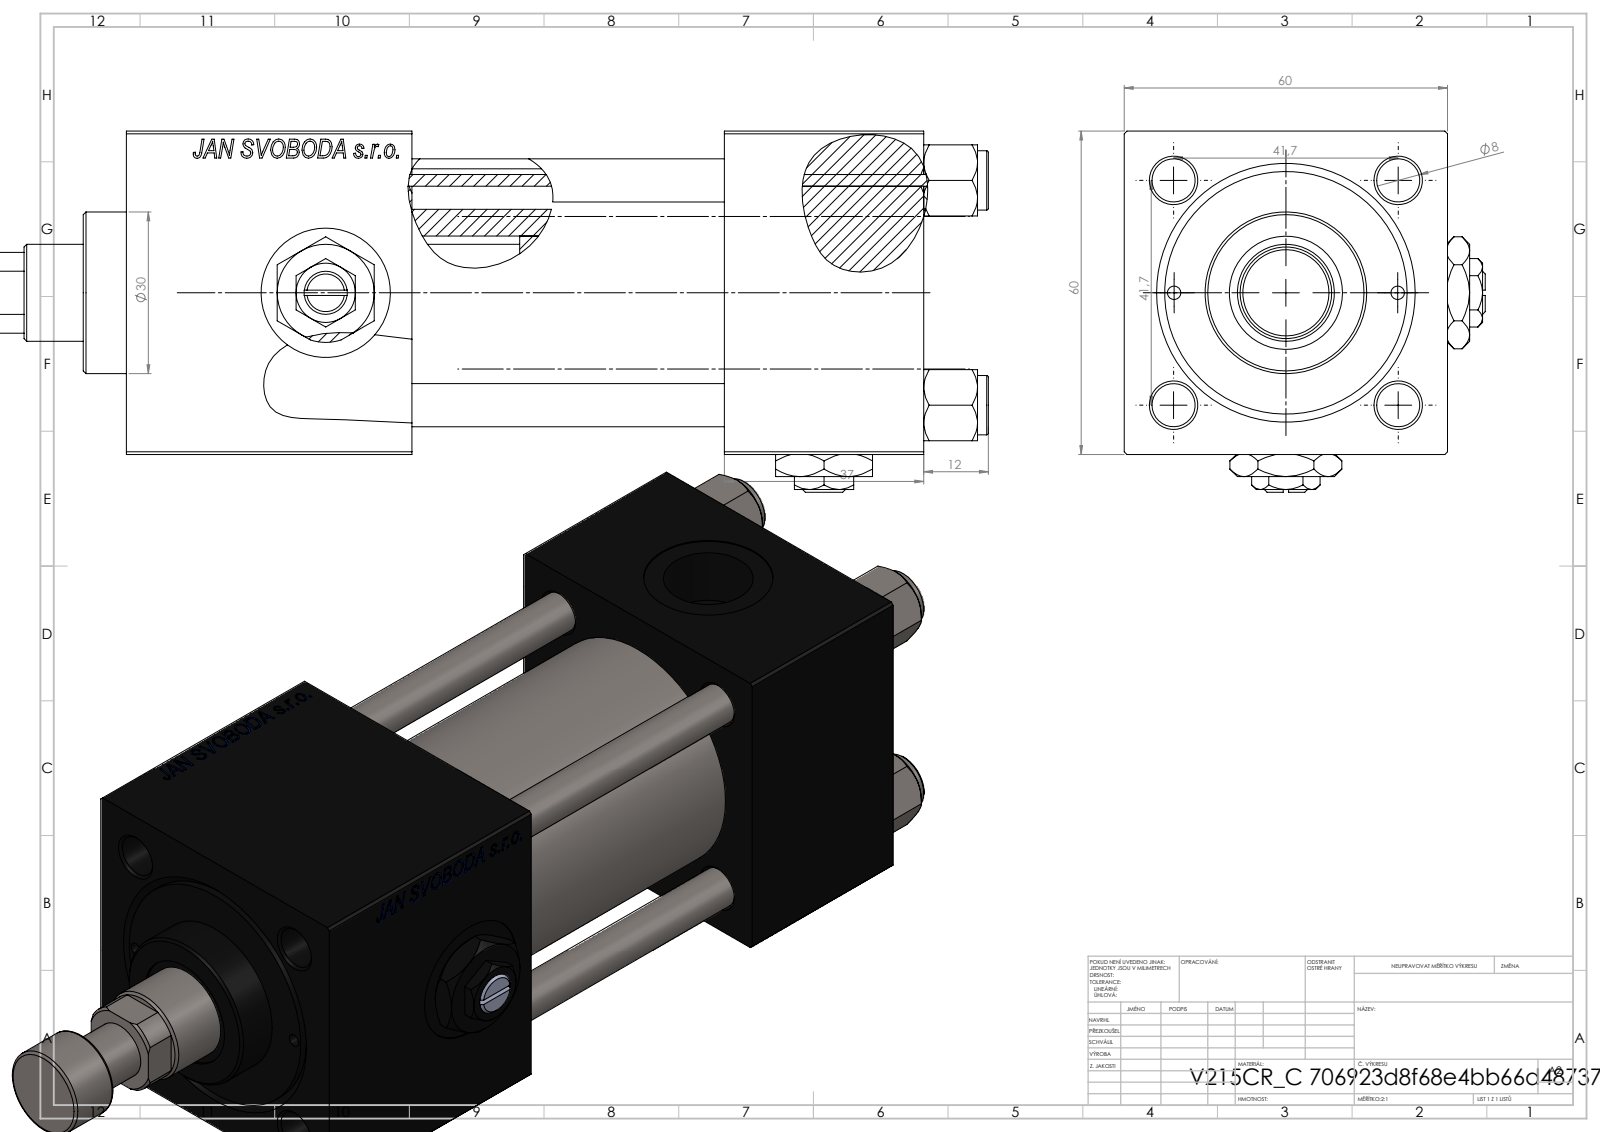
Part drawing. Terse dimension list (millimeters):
name: V215CR_VCP_C; Zatka_pro_OIL_PORT; V215CR_C_Body; V215CR_C_TYCINKA (+3 more)
written by: SolidWorks 2019 (CONFIG_CONTROL_DESIGN)
unit: mm
bodies: 14 solids, 1267 faces (579 planar, 106 cylindrical, 582 other)
size: 205 × 67 × 67
volume: 402 006 mm³; area: 109 724 mm²
holes: 4× ⌀8, 2× ⌀2.5, 2× ⌀7, 2× ⌀16.66, 2× ⌀24, 1× ⌀8.5, 1× ⌀18, 1× ⌀21, 1× ⌀31, 1× ⌀40, 1× ⌀45
bosses: 5× ⌀11, 1× ⌀46, 1× ⌀30, 1× ⌀17
face distances: 60, 37, 53, 148, 111, 58, 95, 119.3, 82.3, 24.3
hole spacings: 20.85, 29.49, 41.7, 46.53, 20.75, 58.97, 41.5
